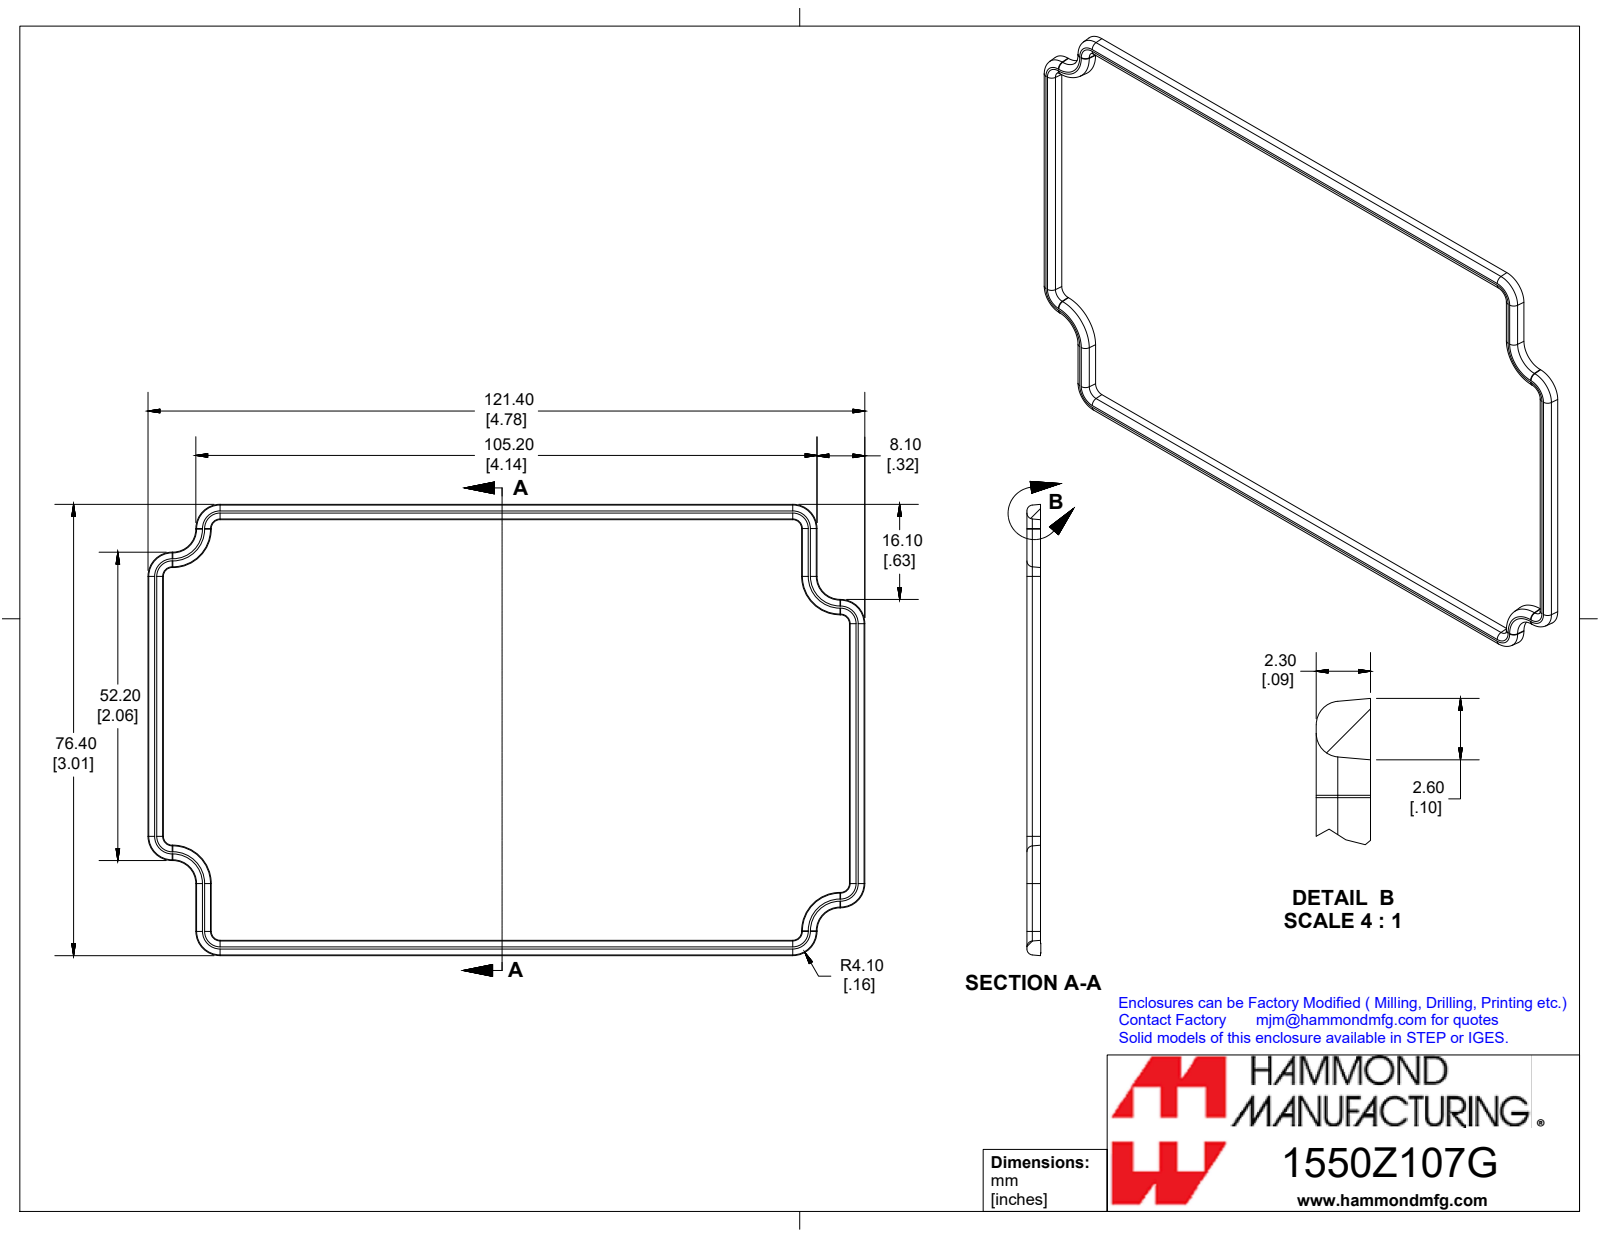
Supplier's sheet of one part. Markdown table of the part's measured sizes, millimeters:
| quantity | value |
| --- | --- |
| part name | 1550Z107GASKET |
| STEP written by | SolidWorks 2019 (CONFIG_CONTROL_DESIGN) |
| units | millimeters |
| bodies | 1 solid, 158 faces (40 planar, 24 cylindrical, 94 other) |
| overall size | 121.4 × 76.4 × 2.4 |
| volume | 1 900 mm³ |
| surface area | 3 197 mm² |
| partial cylindrical surfaces (radius × count) | 1 × 20 |
| main face-to-face distances | 73.5, 2.3, 118.3, 8.1, 110.3, 102.2, 2.4, 16, 57.5, 65.4 |
